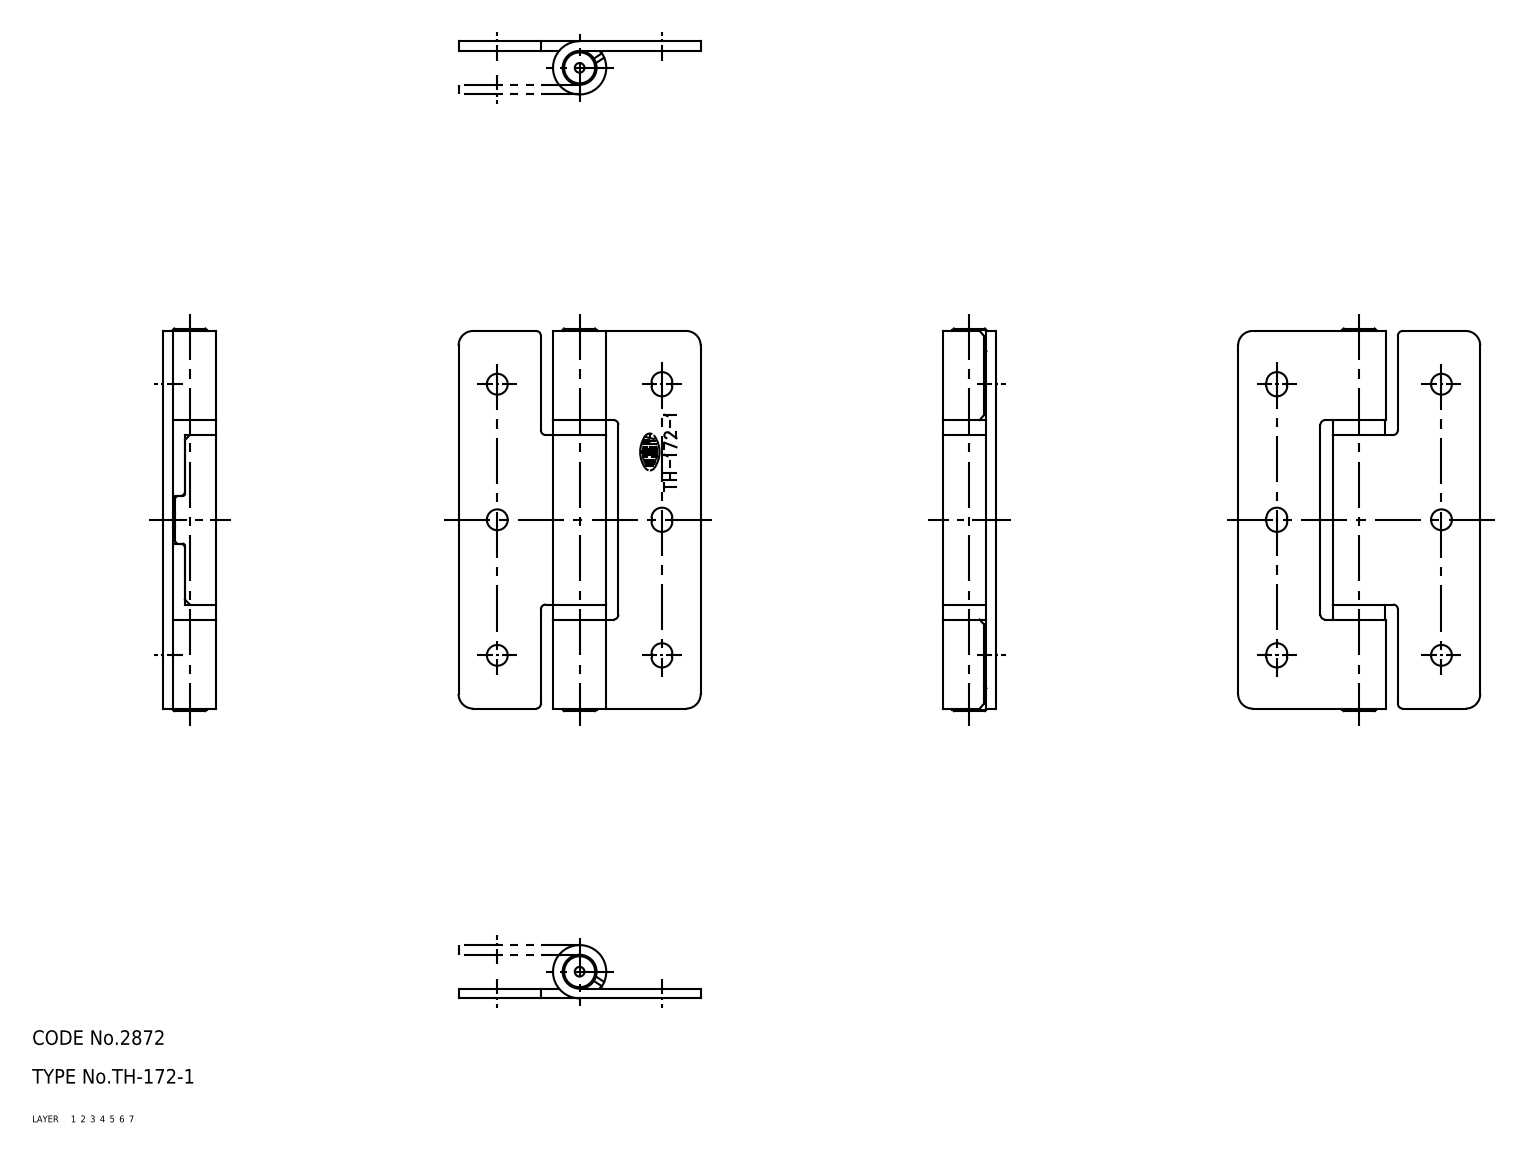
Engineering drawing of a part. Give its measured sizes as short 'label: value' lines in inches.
name: 67115405; 67115418; 67115431; 67115444 (+2 more)
written by: CADfix (AUTOMOTIVE_DESIGN)
unit: in
bodies: 6 solids, 116 faces (0 planar, 0 cylindrical, 116 other)
size: 3.11 × 1.969 × 0.433
volume: 0.774 in³; area: 22.37 in²
